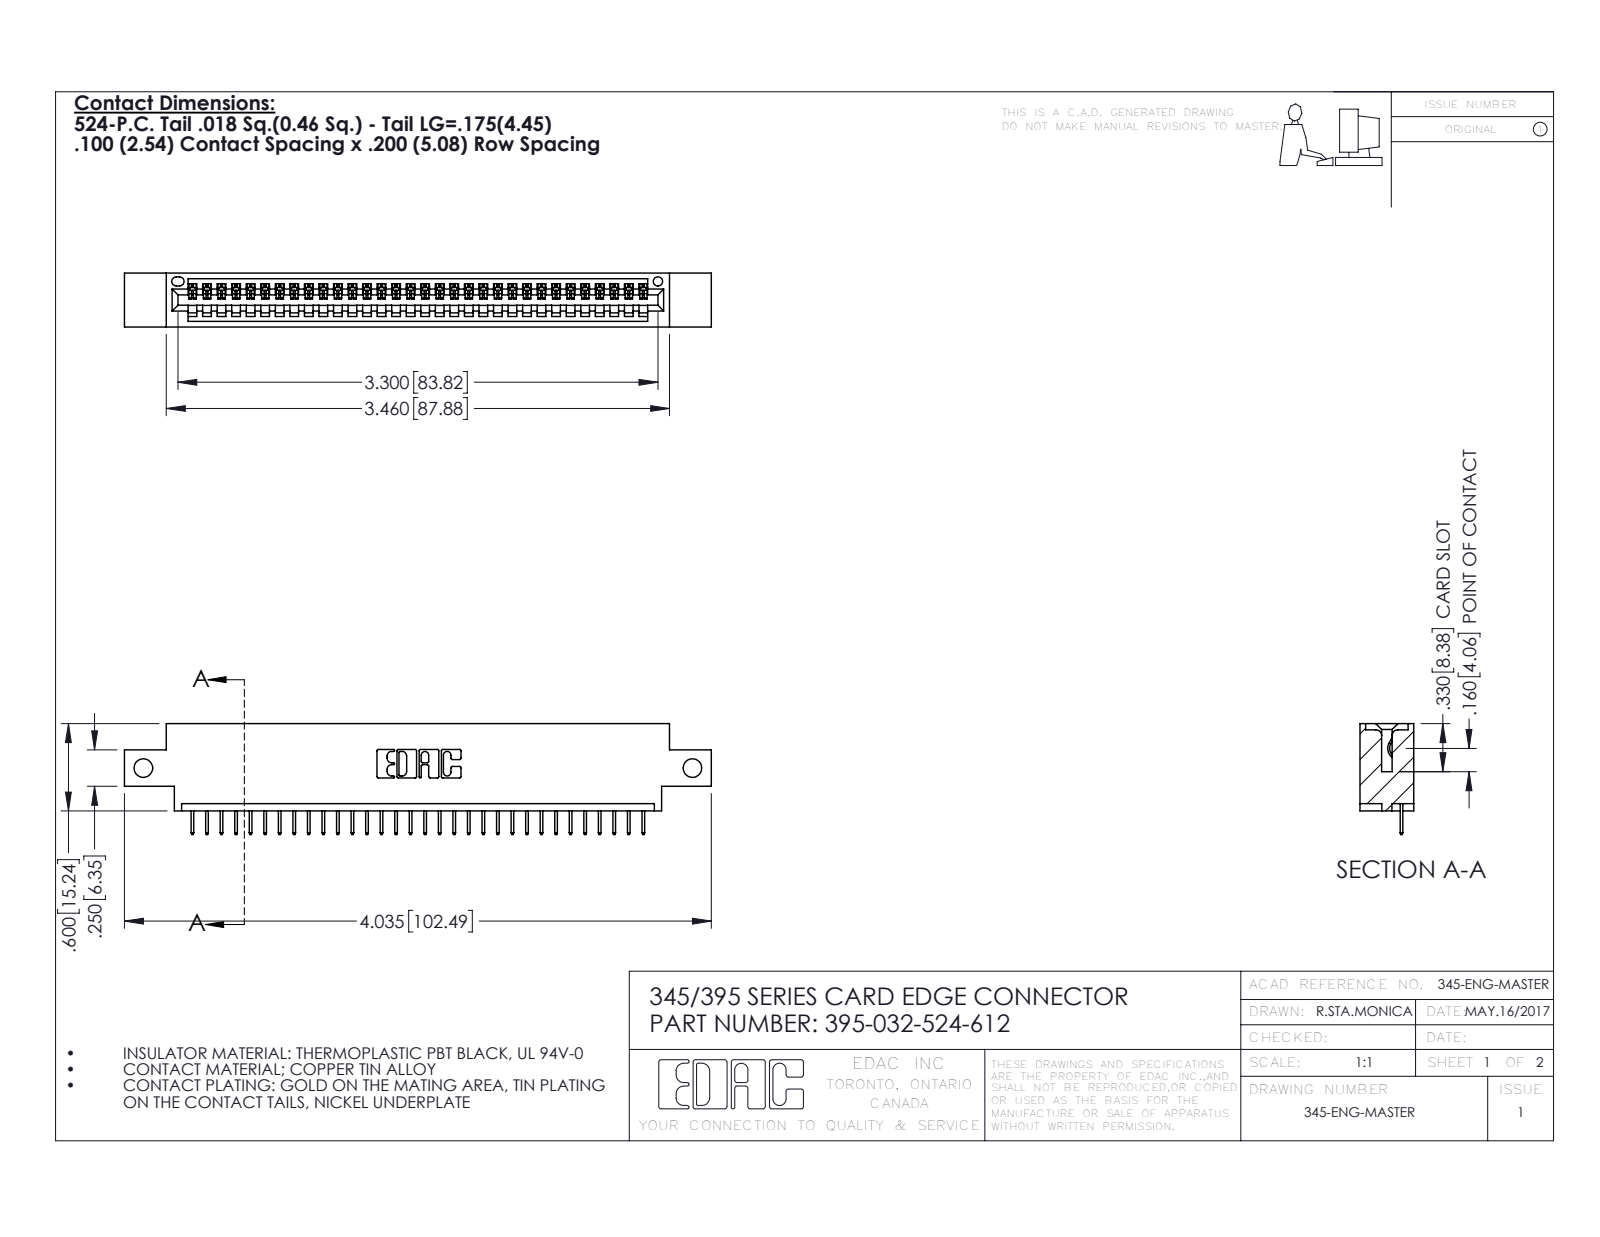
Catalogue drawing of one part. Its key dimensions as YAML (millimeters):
part_name: "345 Part_0.170 Offset - Side Mount; 395-032-524-612; 345-292-001_345-293-124"
step_written_by: "SolidWorks 2016 (CONFIG_CONTROL_DESIGN)"
units: millimeters
bodies: {solids: 33, faces: 2114, planar: 1556, cylindrical: 558, other: 0}
overall_size: [102.5, 19.4, 9.4]
volume: 9320
surface_area: 11840
round_holes:
  - {diameter: 3.3, count: 2}
  - {diameter: 1.6, count: 1}
partial_cylinders:
  - {radius: 0.2, count: 64}
  - {radius: 0.3, count: 22}
  - {radius: 0.2, count: 6}
  - {radius: 0.8, count: 6}
  - {radius: 0.7, count: 3}
  - {radius: 0.8, count: 2}
  - {radius: 1, count: 2}
  - {radius: 0.4, count: 1}
face_to_face_distances: [1.8, 7.6, 9.4, 5.1, 2.5, 6.9, 0.6, 5.7, 1.8, 4.4]
hole_center_spacings: [95.9]
